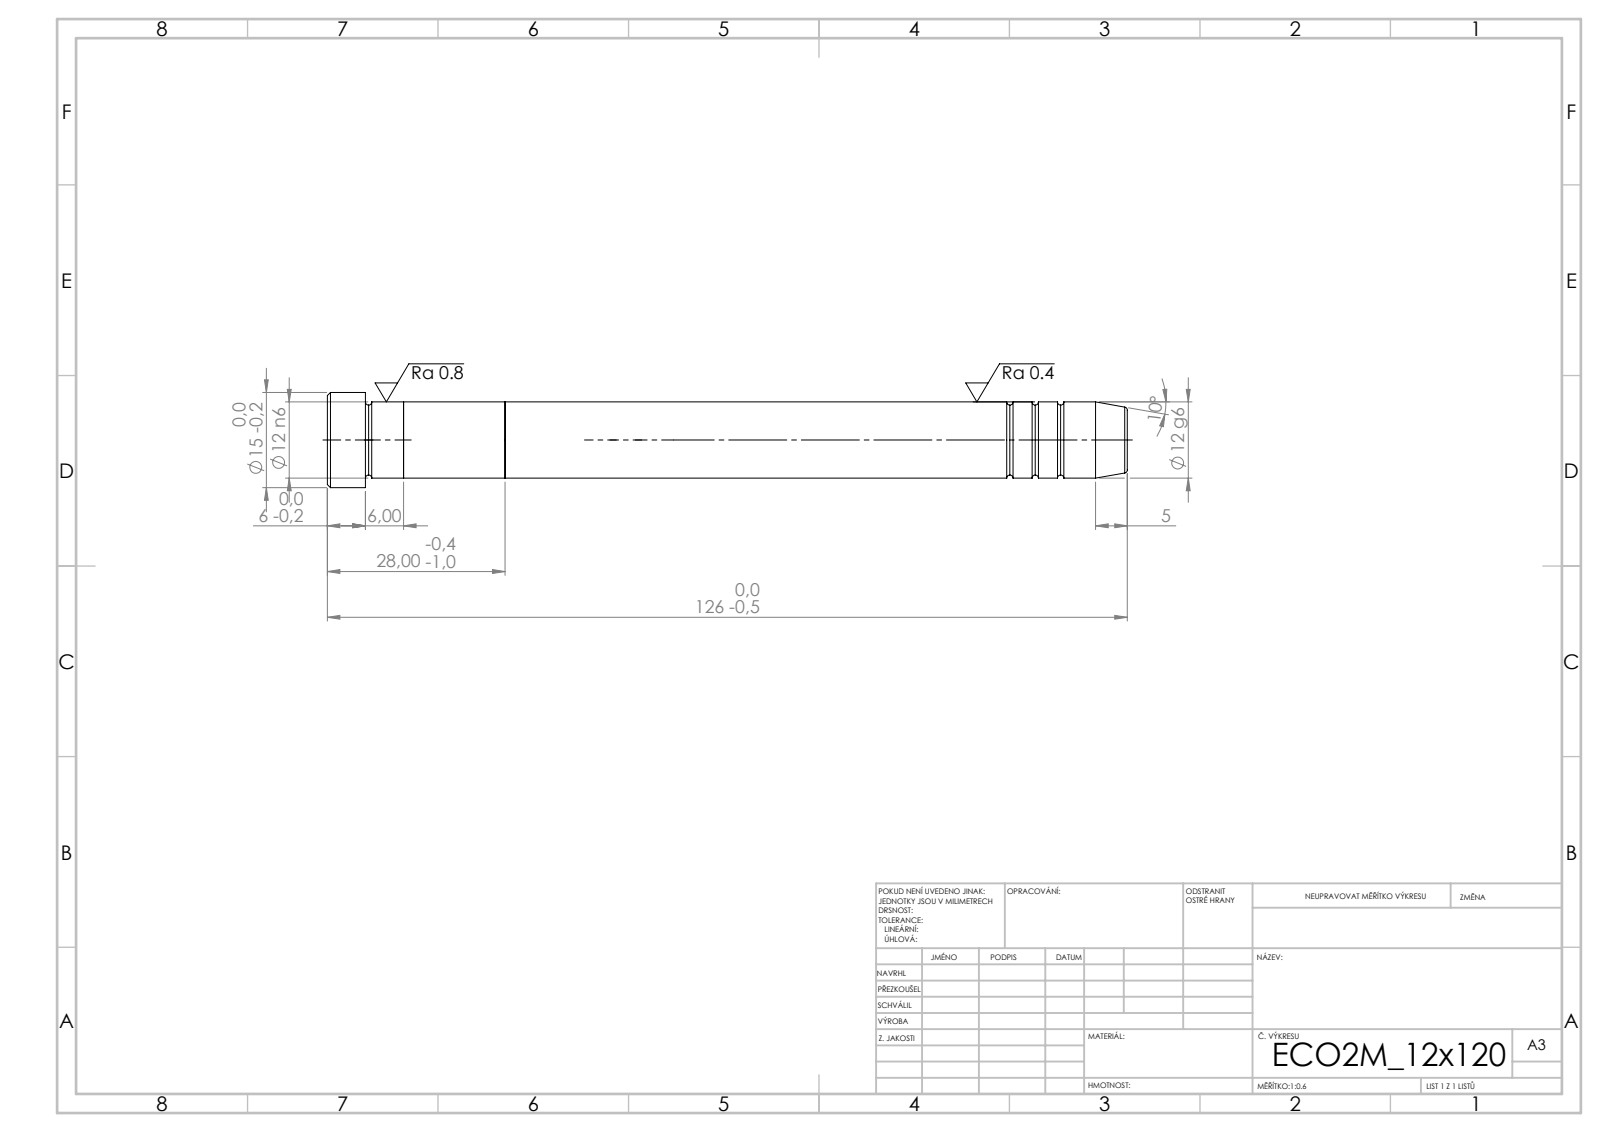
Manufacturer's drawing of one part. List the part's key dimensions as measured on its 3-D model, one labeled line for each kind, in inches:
STEP written by: SolidWorks 2019 (CONFIG_CONTROL_DESIGN)
Units: inches
Bodies: 3 solids, 43 faces (7 planar, 14 cylindrical, 22 other)
Overall size (bounding box): 4.961 × 0.591 × 0.591
Volume: 0.884 in³ · Surface area: 8.719 in²
Round bosses / shafts (diameter × count): ⌀0.591 ×1, ⌀0.472 ×1
Main face-to-face distances: 0.63, 1.102, 0.472, 0.236, 3.858, 4.488, 4.961, 4.724, 0.866
